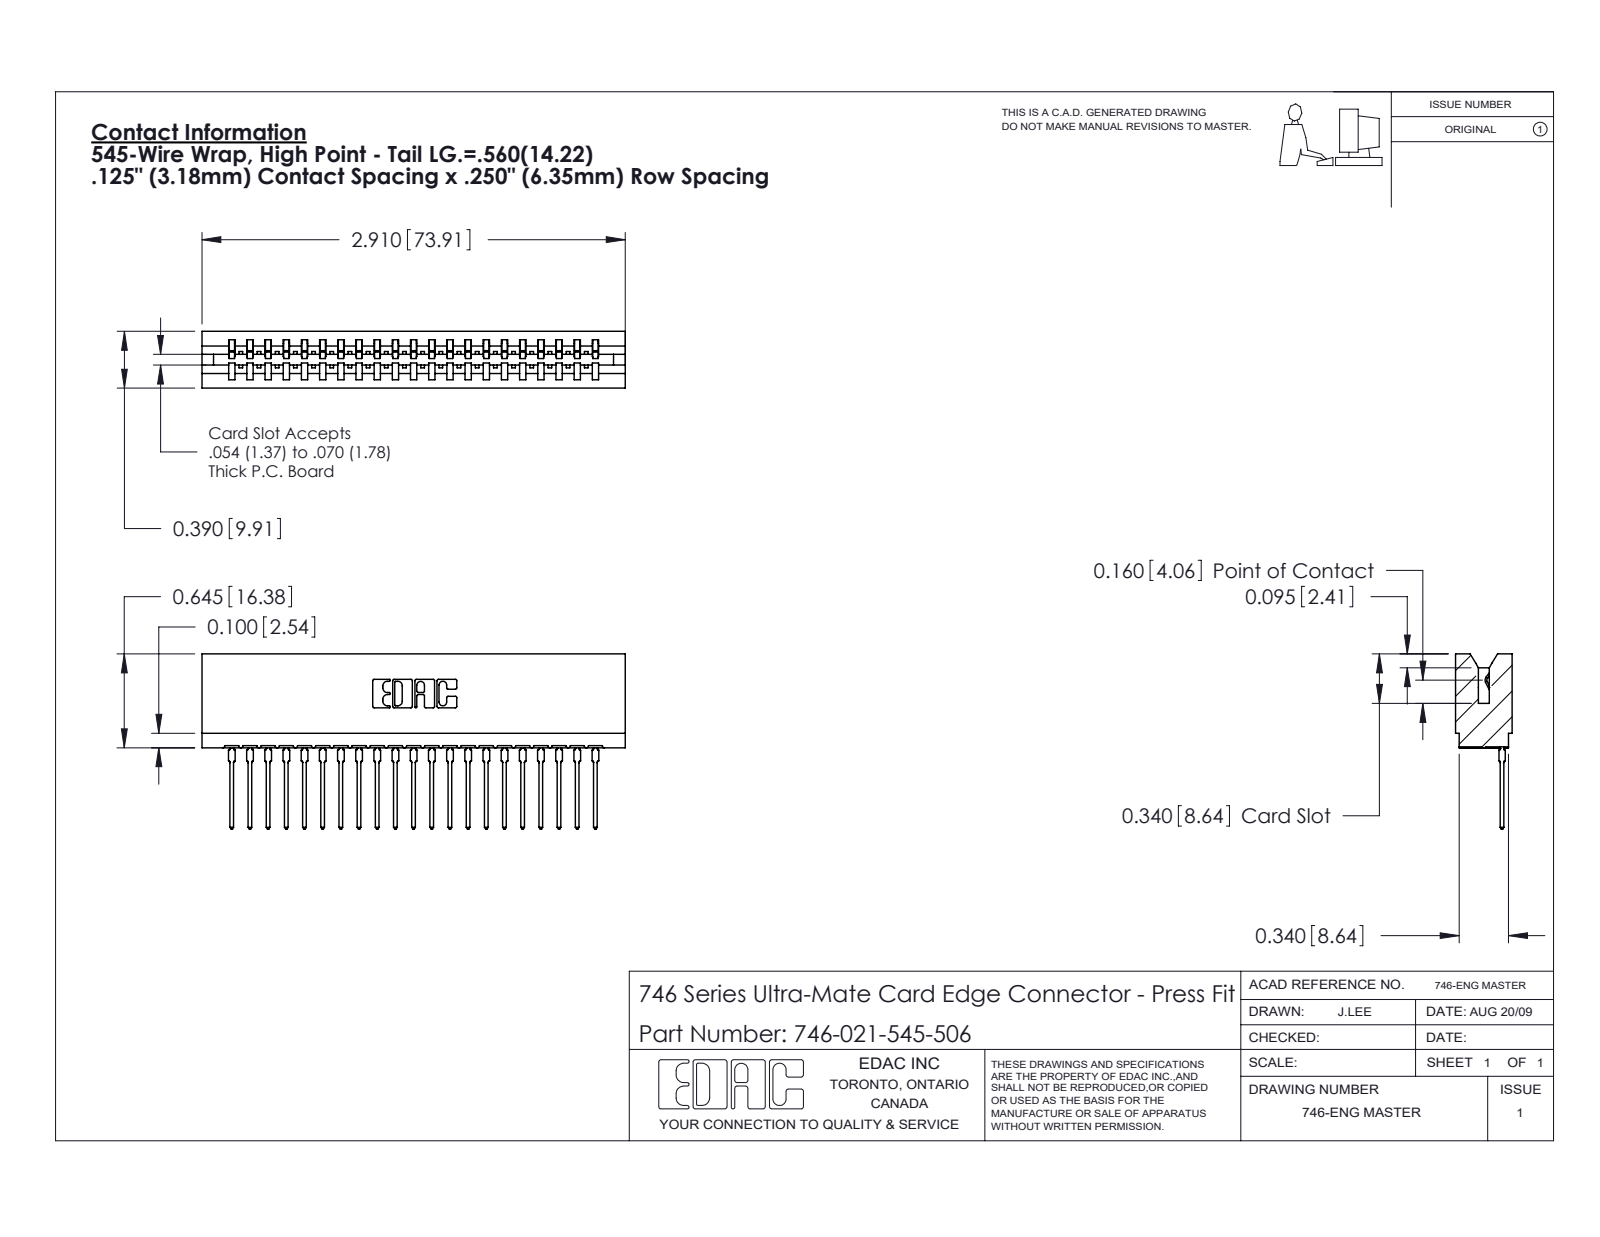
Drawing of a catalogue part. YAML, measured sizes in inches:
part_name: "746 Part_.340 Slot Depth - 06; 746-021-545-506; 746-292-001_545"
step_written_by: "SolidWorks 2020 (CONFIG_CONTROL_DESIGN)"
units: inches
bodies: {solids: 22, faces: 2366, planar: 1379, cylindrical: 441, other: 546}
overall_size: [2.91, 1.204, 0.39]
volume: 0.516
surface_area: 17.67
partial_cylinders:
  - {radius: 0.021, count: 42}
  - {radius: 0.01, count: 22}
  - {radius: 0.015, count: 22}
  - {radius: 0.007, count: 6}
  - {radius: 0.031, count: 6}
  - {radius: 0.005, count: 4}
  - {radius: 0.011, count: 4}
  - {radius: 0.026, count: 3}
face_to_face_distances: [0.333, 0.25, 0.057, 0.39, 0.5, 0.025, 0.307, 0.083, 0.042, 0.125]
